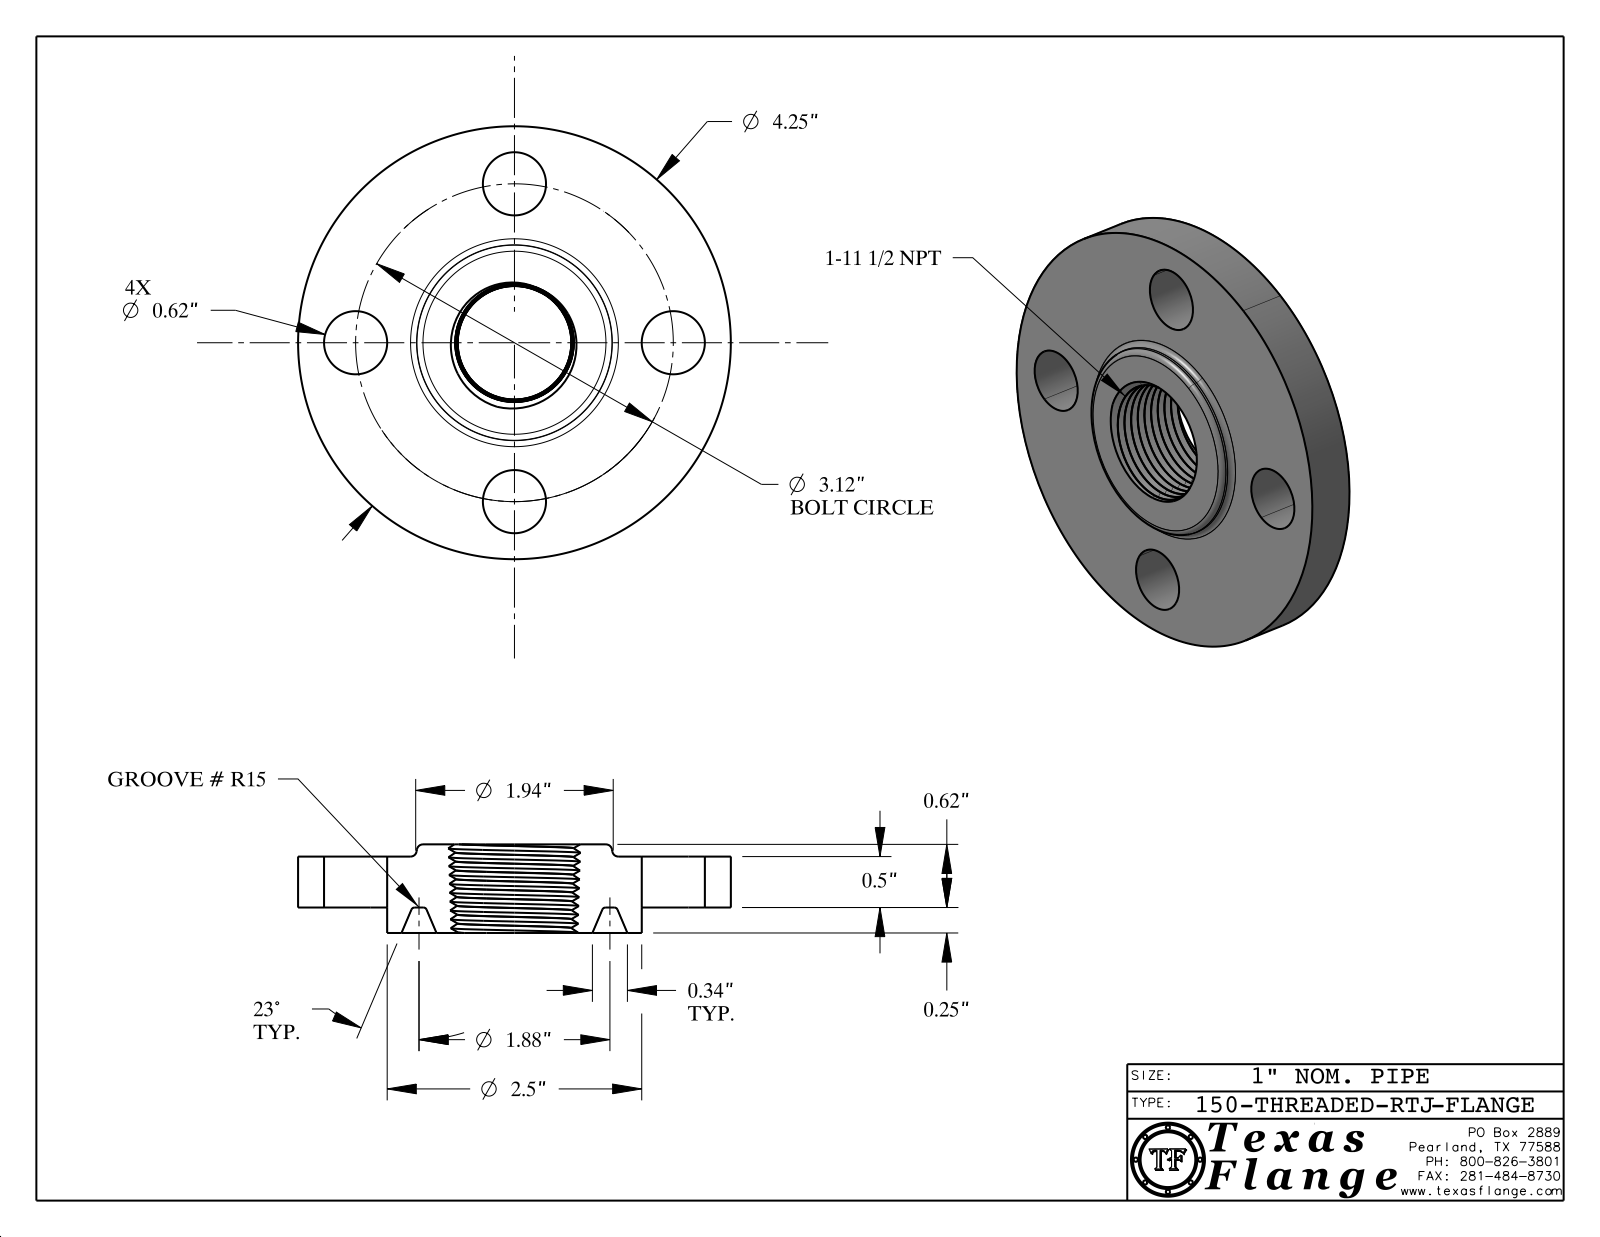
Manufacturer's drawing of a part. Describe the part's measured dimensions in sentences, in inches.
The part is named "150-THREADED-RTJ". Its 3-D file was written by "CATIA V5 STEP AP214 (AUTOMOTIVE_DESIGN)". It is 1 solid with 524 faces: 371 planar, 32 cylindrical and 121 other. Overall it measures 4.25 by 4.25 by 0.87 inches. Its volume is 6.717 cubic inches and its surface area 44.76 square inches. Round holes: 4 of diameter 0.62, 1 of diameter 0.495. Round bosses or shafts: 8 of diameter 0.03, 1 of diameter 4.25, 1 of diameter 2.5, 1 of diameter 0.39. The main face-to-face distances are 0.5, 0.25, 0.75, 0.87, 0.62, 0.12, 0.735, 0.485, 0.015, 0.135. The hole center spacings are 2.206, 1.194, 2.882, 3.12.
